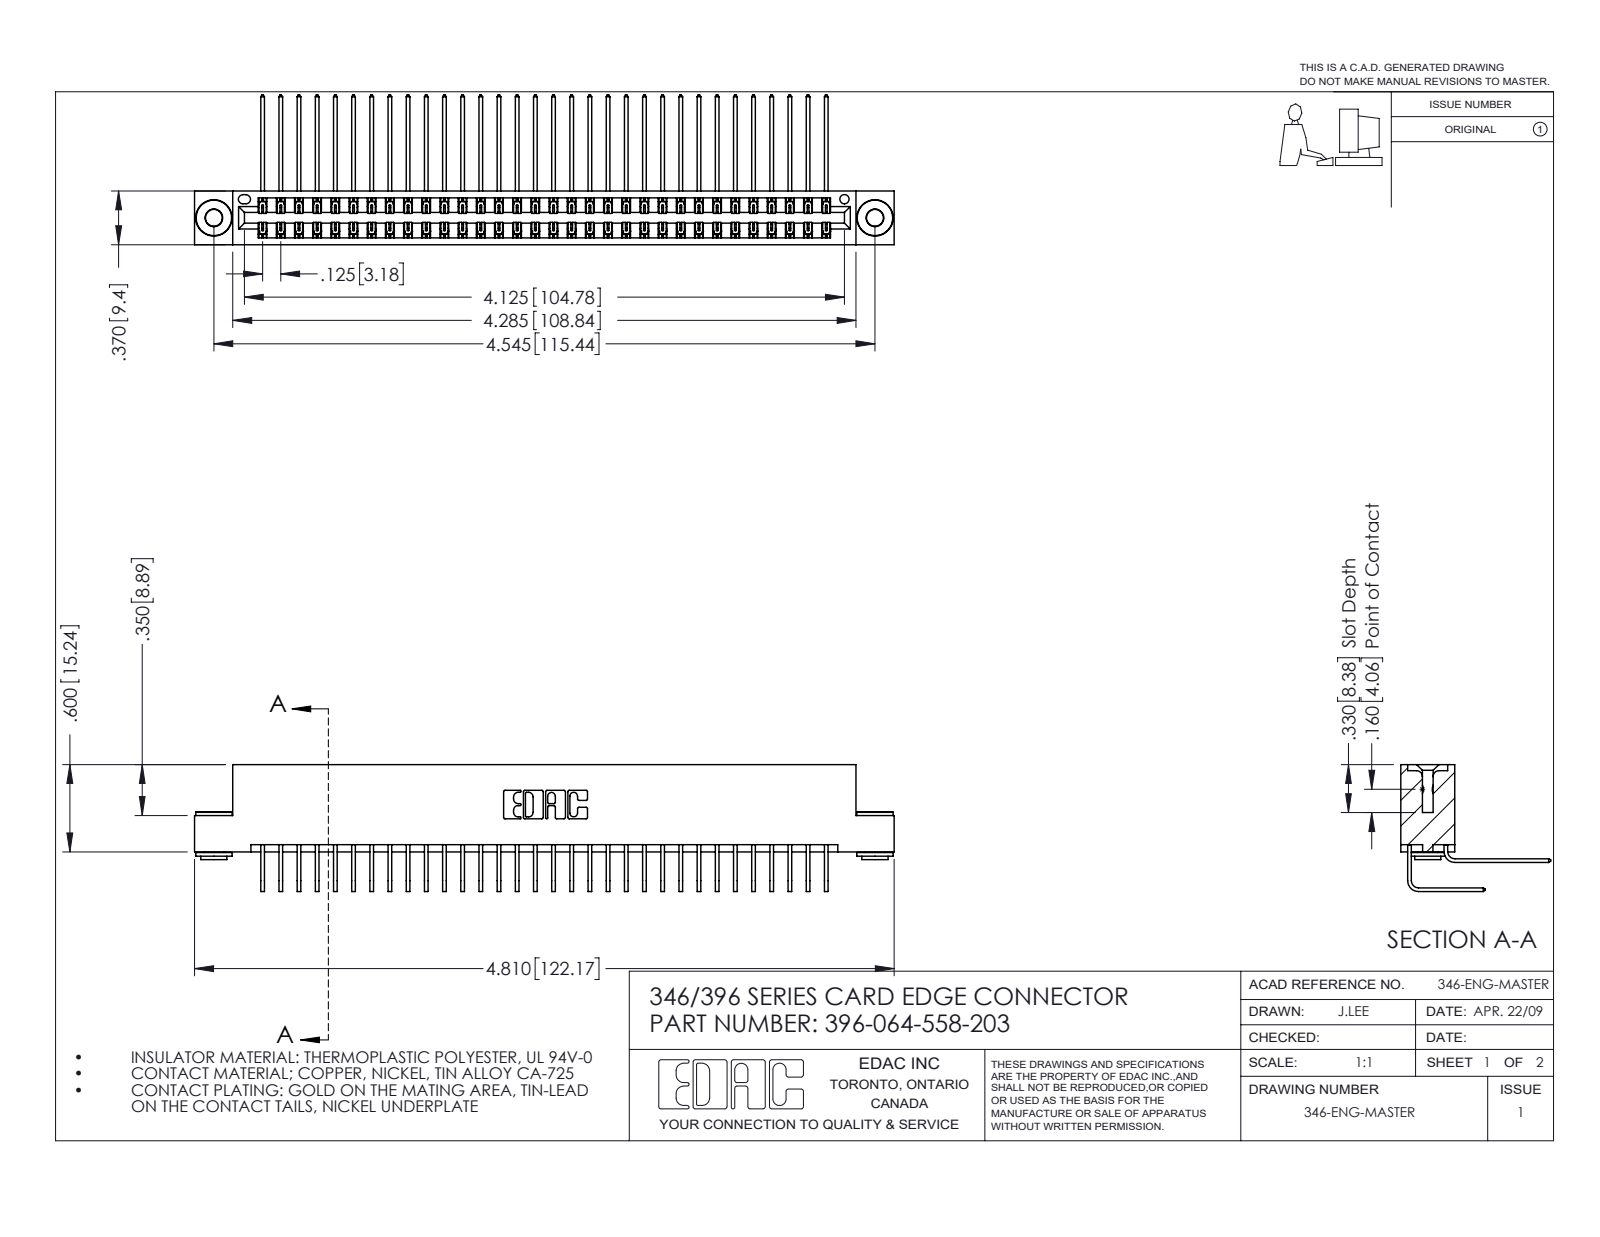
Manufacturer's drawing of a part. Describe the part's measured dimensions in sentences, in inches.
The part is named "345-292-001_558 559 Tail - 1; 396-064-558-203; 346 Part_Flush Mounting Lugs - 0.156 Dia-TH; 345-292-001_558 Tail - 2 (+1 more)". Its 3-D file was written by "SolidWorks 2016 (CONFIG_CONTROL_DESIGN)". It is 67 solids with 3616 faces: 2454 planar, 1154 cylindrical and 8 other. Overall it measures 4.81 by 1.03 by 0.873 inches. Its volume is 0.746 cubic inches and its surface area 28.88 square inches. Round holes: 2 of diameter 0.116, 2 of diameter 0.156, 1 of diameter 0.064. Round bosses or shafts: 2 of diameter 0.25, 2 of diameter 0.18, 2 of diameter 0.136. Partial cylindrical surfaces (rounded edges, fillets, slot ends): 96 of radius 0.006, 22 of radius 0.01, 6 of radius 0.007, 6 of radius 0.031, 3 of radius 0.026, 2 of radius 0.014, 2 of radius 0.022, 2 of radius 0.024. The main face-to-face distances are 0.322, 0.048, 0.025, 0.25, 0.37, 0.298, 0.072, 0.275, 0.148, 0.222. The hole center spacings are 0.246, 4.337, 4.545.
